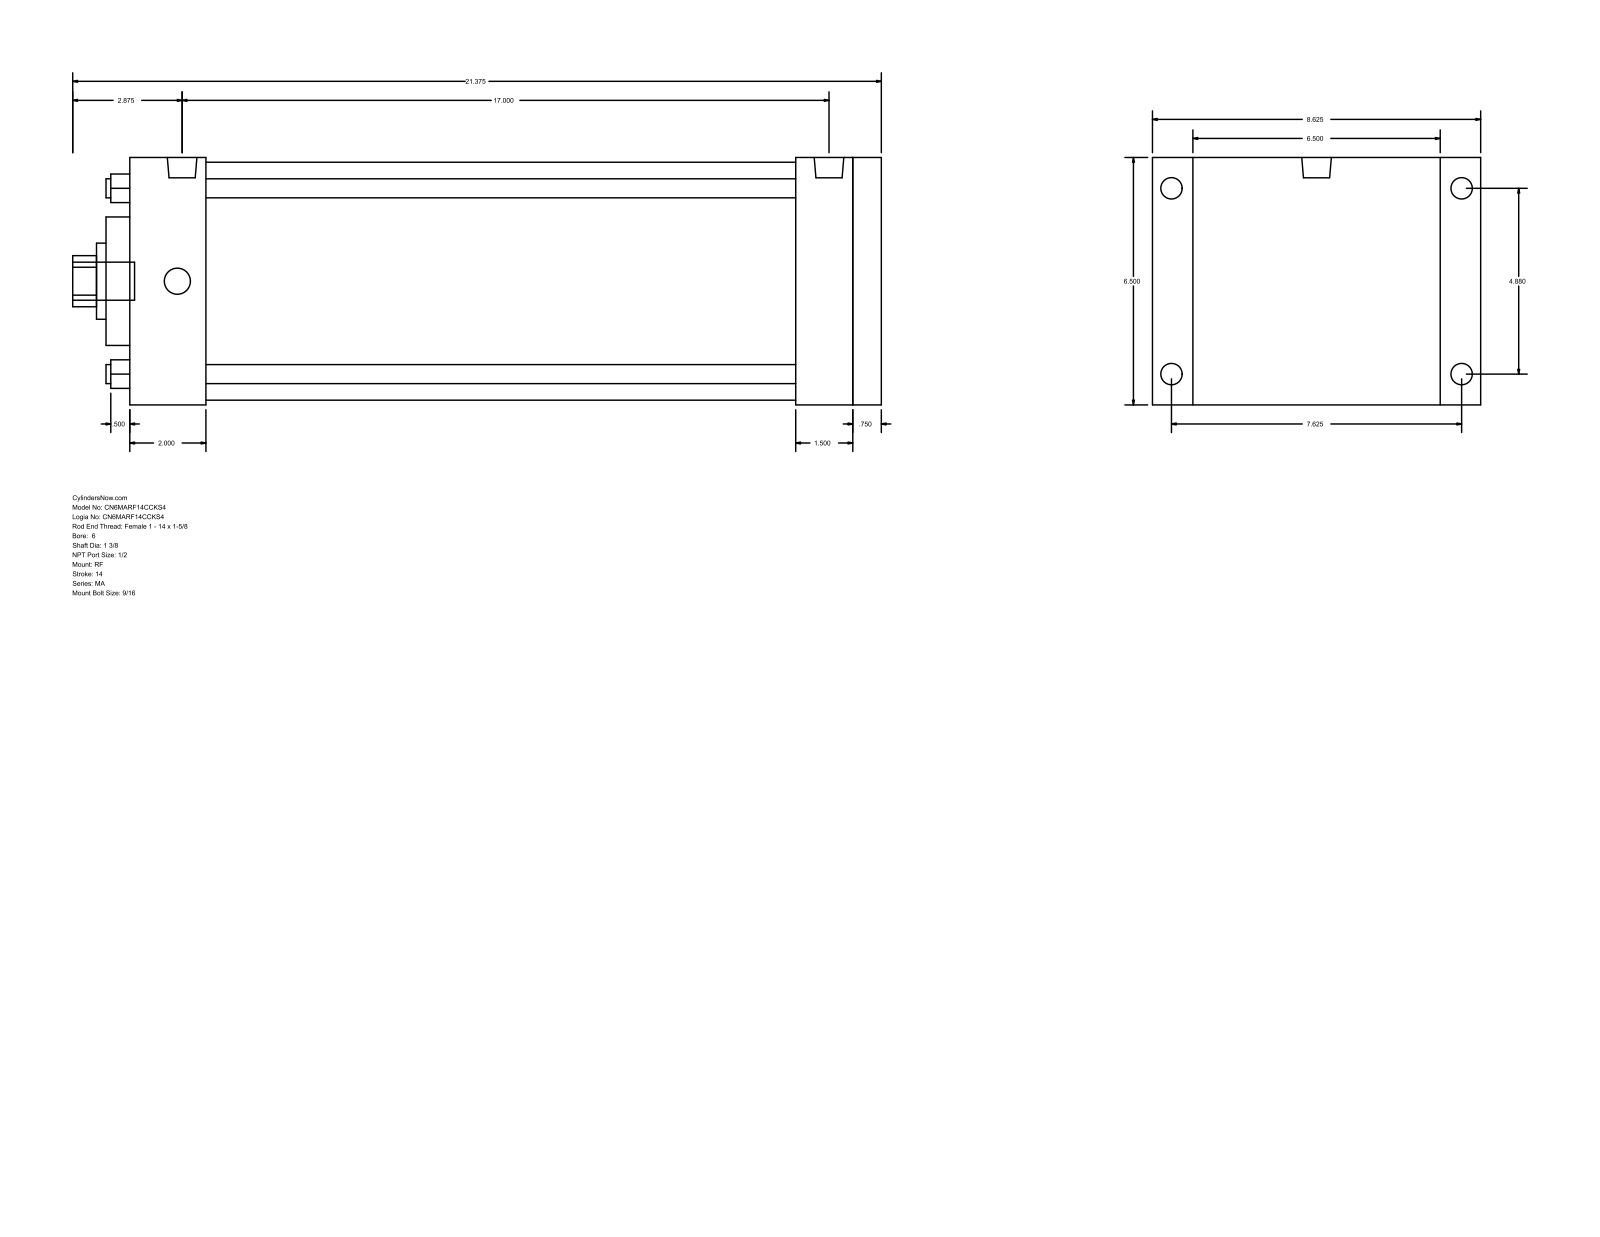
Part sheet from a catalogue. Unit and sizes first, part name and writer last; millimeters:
Units: millimetres
Overall size (bounding box): 542.92 × 219.07 × 165.1
Round holes (diameter × count): ⌀12.7 ×4, ⌀34.92 ×1, ⌀50.8 ×1, ⌀85.72 ×1, ⌀158.75 ×1
Round bosses / shafts (diameter × count): ⌀17.46 ×4, ⌀14.29 ×4, ⌀19.77 ×2, ⌀25.4 ×1
Partial cylindrical surfaces — rounded edges, fillets, slot ends (radius × count): R17.06 ×1
Main face-to-face distances: 165.1, 504.82, 19.04, 485.78, 50.8, 434.98, 454.02, 447.67, 396.87, 38.11
Hole centre spacings: 87.65, 123.96, 175.31
Bodies: 0 solids, 94 faces (65 planar, 29 cylindrical, 0 other)
Part name (STEP PRODUCT): MA_RF__0600_1.375
STEP written by: GSSL Pune (CONFIG_CONTROL_DESIGN)
